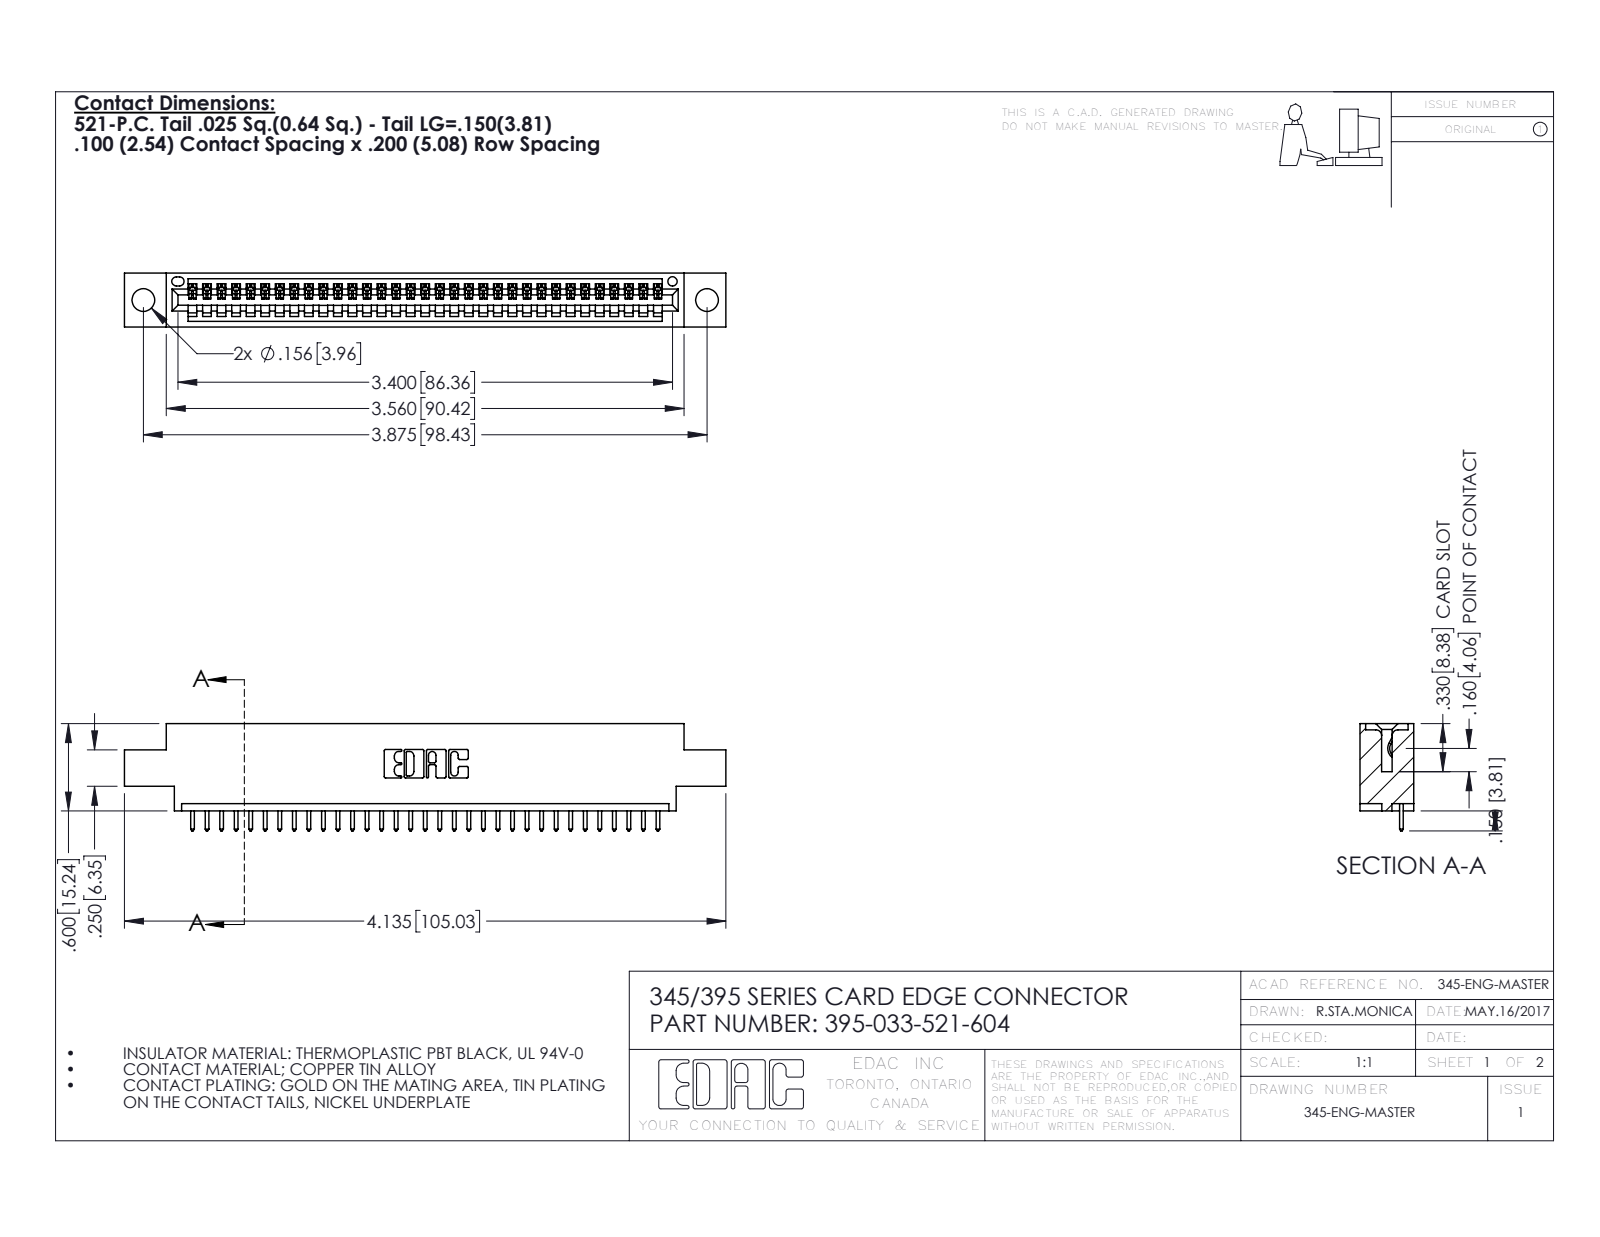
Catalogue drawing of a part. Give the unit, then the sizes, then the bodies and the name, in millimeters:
Units: millimetres
Overall size (bounding box): 105 × 18.7 × 9.4
Round holes (diameter × count): ⌀4 ×2, ⌀1.6 ×1
Partial cylindrical surfaces — rounded edges, fillets, slot ends (radius × count): R0.2 ×66, R0.3 ×66, R0.3 ×22, R0.2 ×6, R0.8 ×6, R0.7 ×3, R0.8 ×2, R1 ×2
Main face-to-face distances: 7.6, 1.8, 9.4, 5.1, 2.5, 6.9, 0.6, 5.7, 4.4, 3.8
Hole centre spacings: 6.9, 92.5, 98.4
Volume: 9 600 mm³ · Surface area: 12 210 mm²
Bodies: 34 solids, 2044 faces (1404 planar, 640 cylindrical, 0 other)
Part name (STEP PRODUCT): 345-292-001_345-293-121; 345 Part_0.170 Offset - 0.156 Dia-TH; 395-033-521-604
STEP written by: SolidWorks 2016 (CONFIG_CONTROL_DESIGN)
